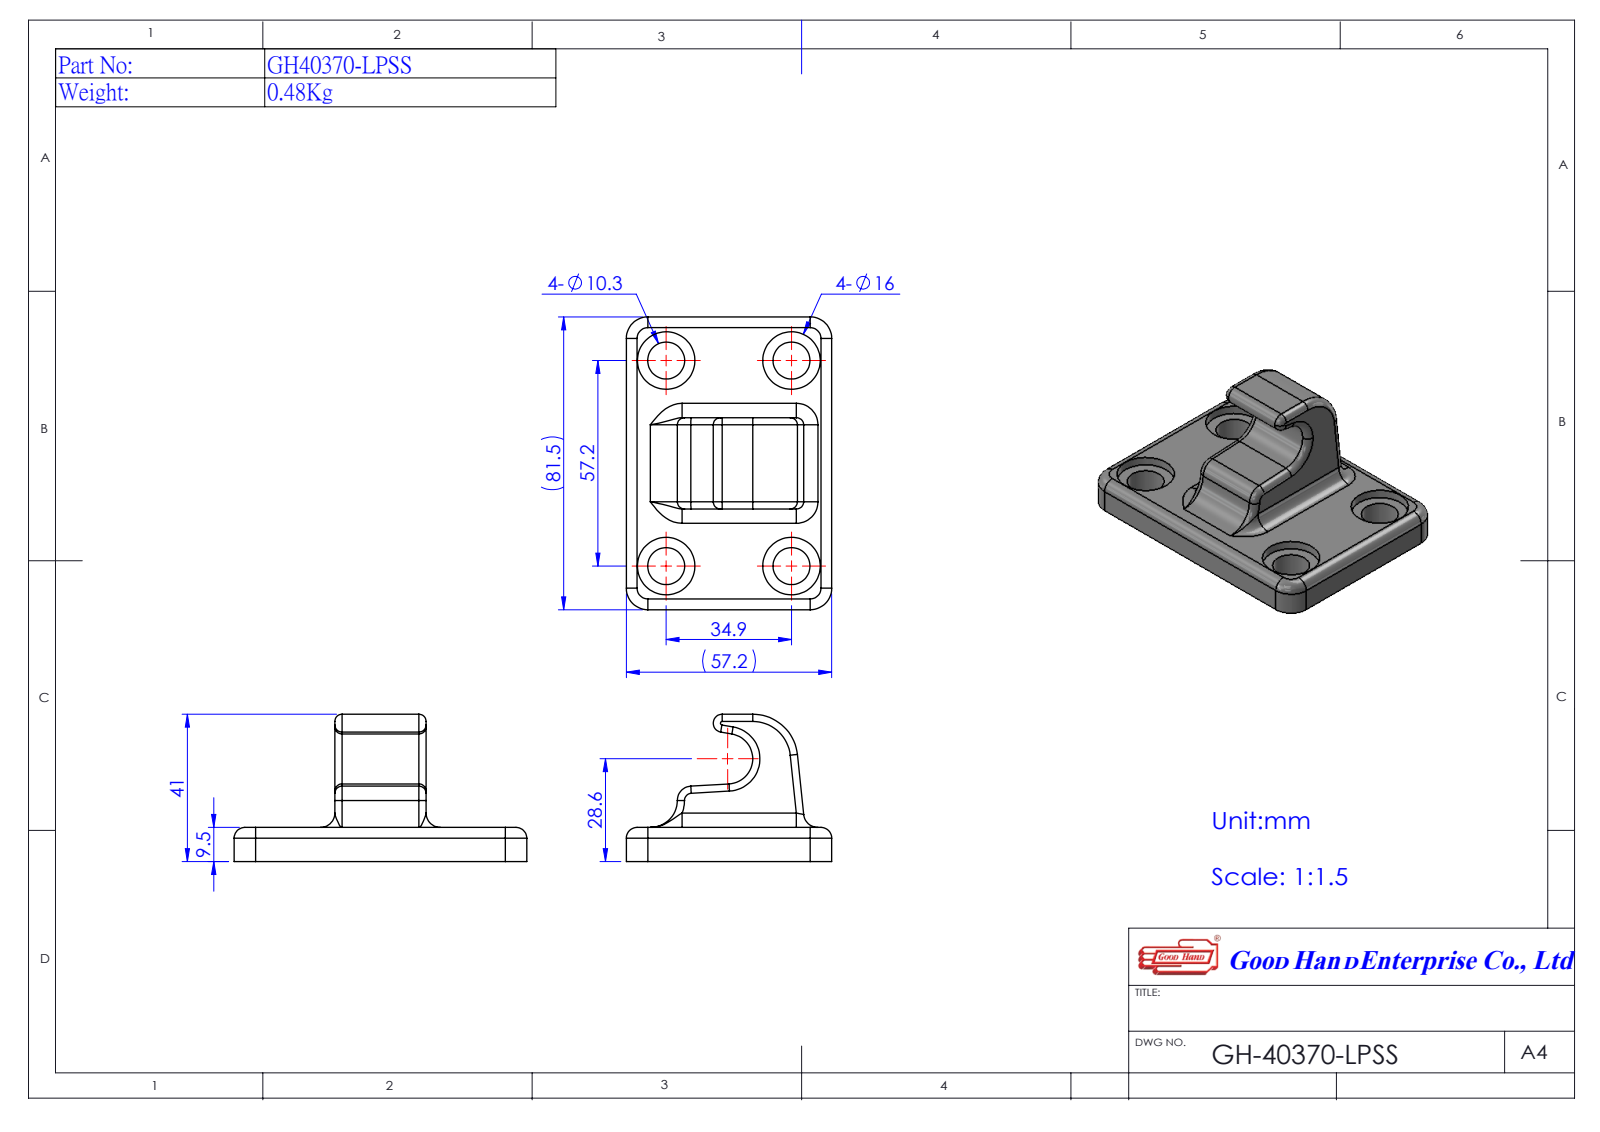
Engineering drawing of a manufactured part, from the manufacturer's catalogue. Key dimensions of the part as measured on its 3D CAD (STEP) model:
Part name (STEP PRODUCT): GH-40370-LPSS
STEP written by: SolidWorks 2016 (AUTOMOTIVE_DESIGN)
Units: millimetres
Bodies: 1 solid, 79 faces (16 planar, 41 cylindrical, 22 other)
Overall size (bounding box): 81.5 × 57.2 × 41
Volume: 57 430 mm³ · Surface area: 14 906 mm²
Round holes (diameter × count): ⌀10.3 ×4, ⌀16 ×4
Partial cylindrical surfaces — rounded edges, fillets, slot ends (radius × count): R2 ×8, R3 ×4, R4 ×4, R6 ×4, R2.5 ×1, R7 ×1, R7.5 ×1, R12.5 ×1
Main face-to-face distances: 9.5, 28.05, 53.45, 7, 2.5, 57.2, 25.4, 81.5, 41, 34
Hole centre spacings: 34.9, 57.2, 67.01
